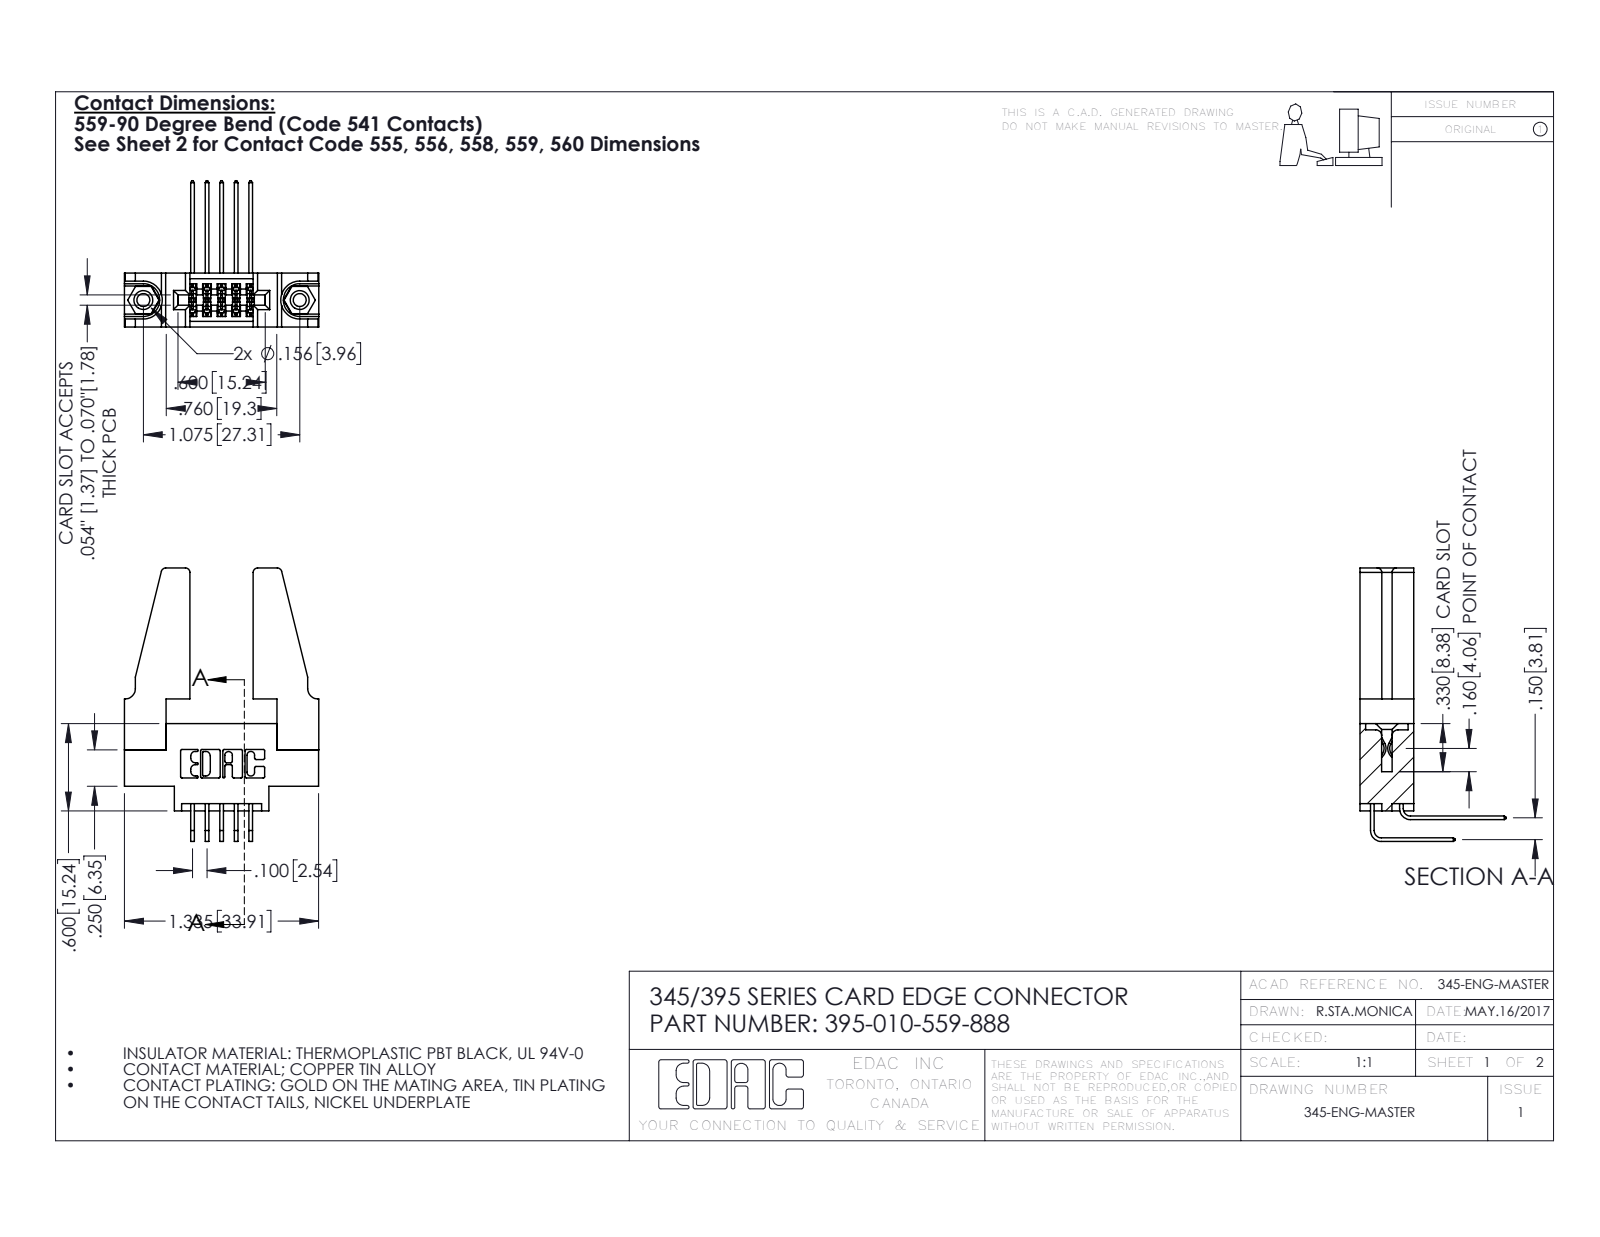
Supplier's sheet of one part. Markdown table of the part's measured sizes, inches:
| quantity | value |
| --- | --- |
| part name | 345-250-001_345-250-001-102; 395-010-559-888; 345-292-001_558 559 Tail - 1; 345-220-078_345-220-088 (+2 more) |
| STEP written by | SolidWorks 2016 (CONFIG_CONTROL_DESIGN) |
| units | inches |
| bodies | 15 solids, 774 faces (506 planar, 252 cylindrical, 16 other) |
| overall size | 1.879 × 1.336 × 1.005 |
| volume | 0.375 in³ |
| surface area | 11.01 in² |
| round holes (diameter × count) | 0.089 × 2, 0.125 × 2, 0.156 × 2, 0.064 × 1 |
| round bosses / shafts (diameter × count) | 0.155 × 2 |
| partial cylindrical surfaces (radius × count) | 0.01 × 22, 0.006 × 16, 0.03 × 8, 0.007 × 6, 0.031 × 6, 0.026 × 3, 0.014 × 2, 0.019 × 2 |
| main face-to-face distances | 0.37, 0.072, 0.298, 0.2, 0.148, 0.15, 0.15, 0.22, 0.077, 0.225 |
| hole center spacings | 0.27, 0.847, 1.075 |
